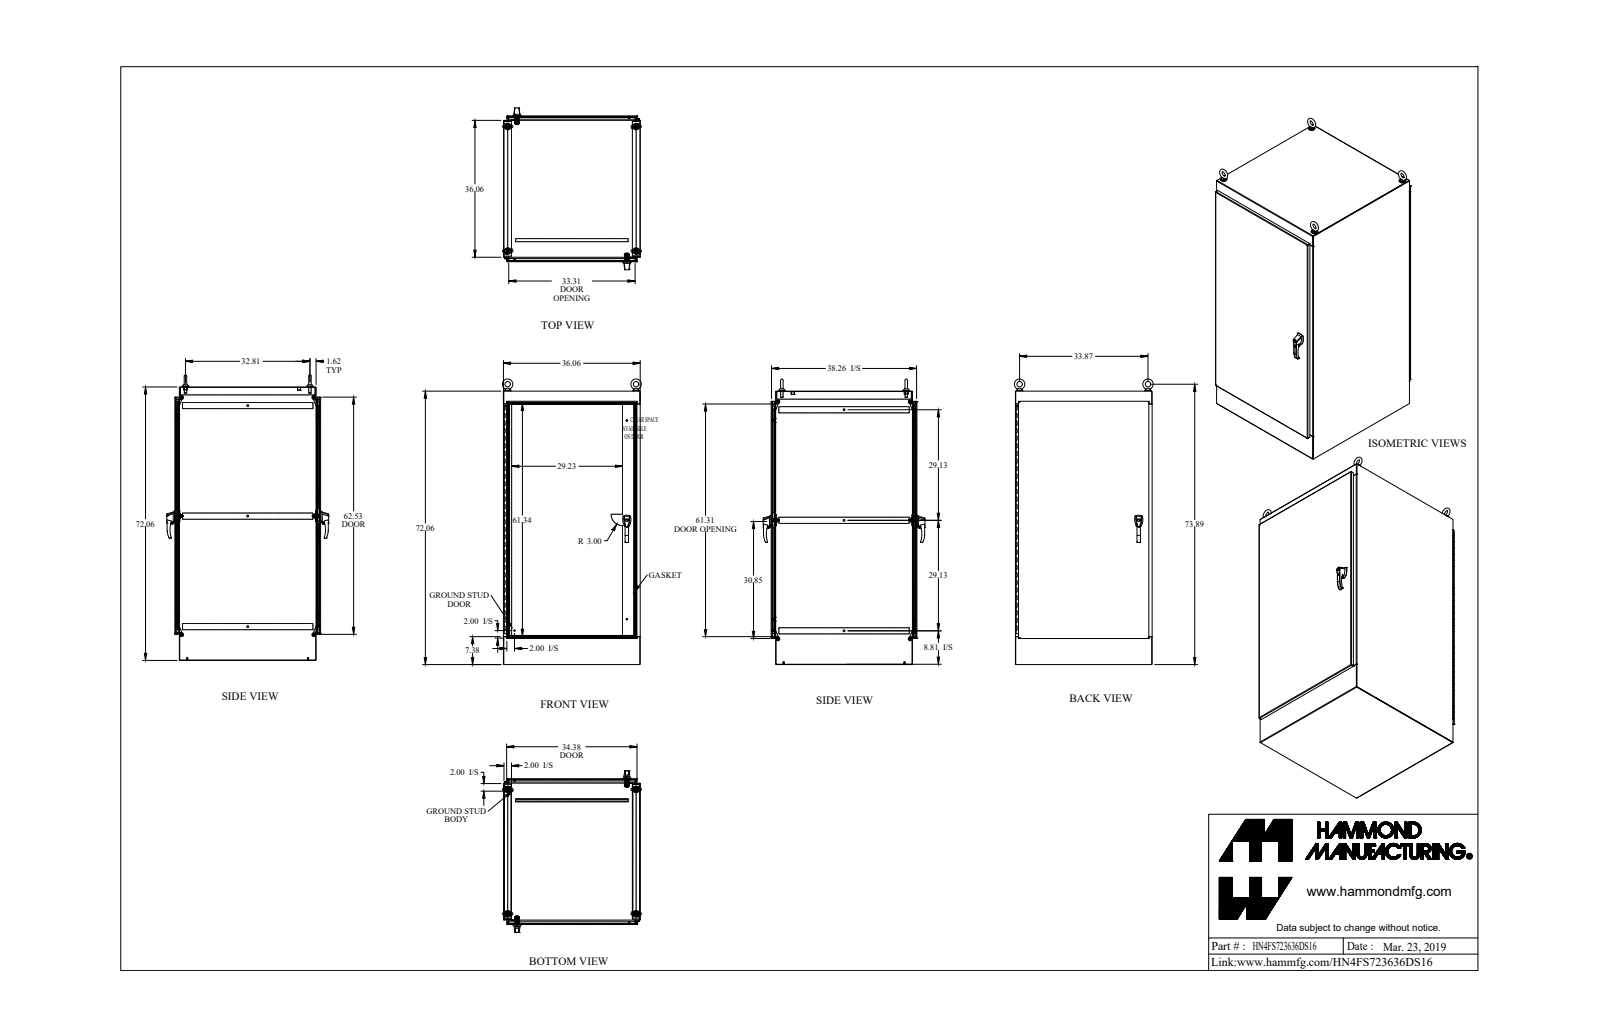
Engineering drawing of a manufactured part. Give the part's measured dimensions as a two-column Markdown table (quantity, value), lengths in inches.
| quantity | value |
| --- | --- |
| part name | HN4FS723636DS16 |
| STEP written by | SolidWorks 2018 (AUTOMOTIVE_DESIGN) |
| units | inches |
| bodies | 95 solids, 3321 faces (1460 planar, 1533 cylindrical, 328 other) |
| overall size | 75.489 × 42.664 × 36.604 |
| volume | 1 564 in³ |
| surface area | 32 832 in² |
| round holes (diameter × count) | 0.304 × 20, 0.35 × 8, 0.25 × 4, 0.257 × 4, 0.28 × 4, 0.281 × 4, 0.313 × 4, 0.39 × 4, 0.413 × 4, 0.625 × 4, 0.68 × 4, 0.75 × 4 |
| round bosses / shafts (diameter × count) | 1.75 × 4, 1.5 × 4, 1.25 × 4, 1 × 4, 0.75 × 4, 0.738 × 4, 0.63 × 4, 0.625 × 4 |
| partial cylindrical surfaces (radius × count) | 0.125 × 44, 0.043 × 42, 0.138 × 36, 0.018 × 32, 0.048 × 26, 0.143 × 26, 0.5 × 26, 0.06 × 21 |
| main face-to-face distances | 0.095, 35.965, 38.339, 35.87, 36.06, 71.965, 38.244, 38.434, 1.187, 37.152 |
| hole center spacings | 6, 34.827, 12, 36.344, 18, 38.742, 24, 41.868 |
